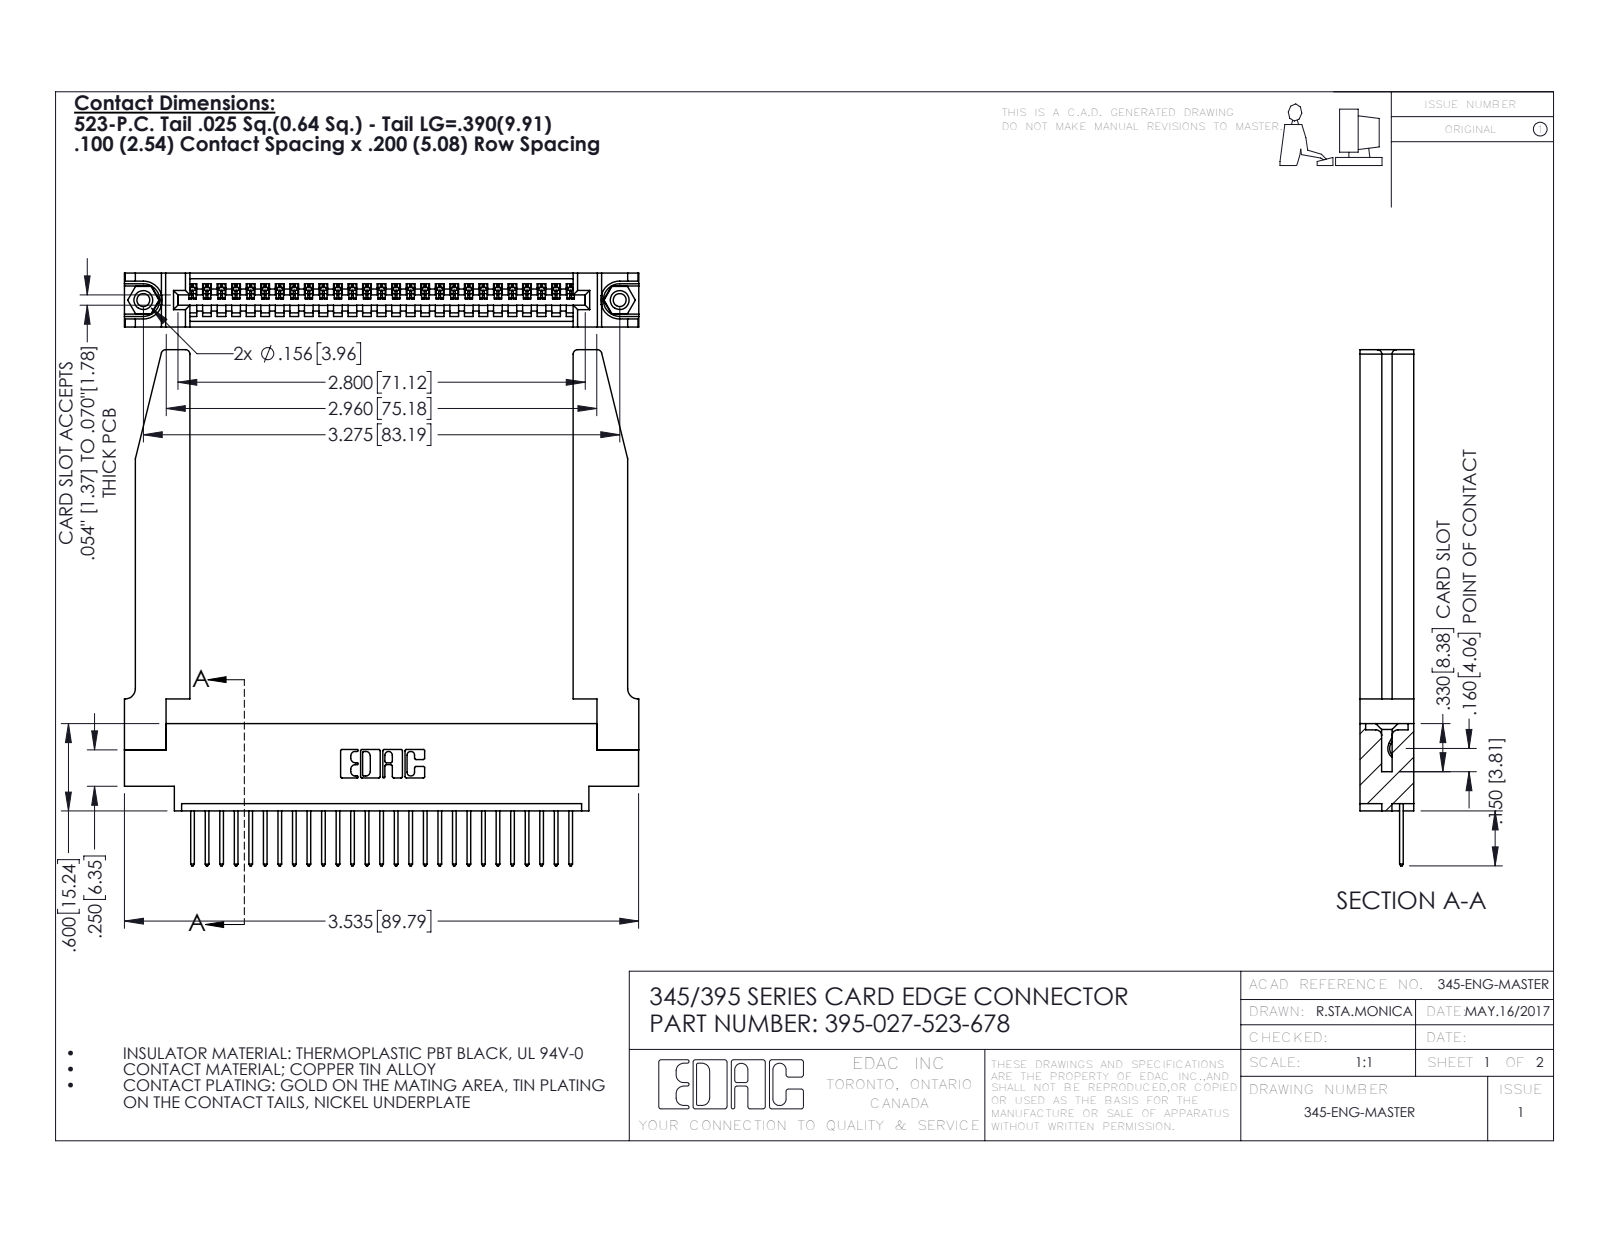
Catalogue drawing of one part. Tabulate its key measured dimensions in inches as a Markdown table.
| quantity | value |
| --- | --- |
| part name | 395-027-523-678; 345-250-001_345-250-001-102; 345-292-001_345-293-123; 345 Part_0.170 Offset - 0.156 Dia-TH (+1 more) |
| STEP written by | SolidWorks 2016 (CONFIG_CONTROL_DESIGN) |
| units | inches |
| bodies | 32 solids, 1930 faces (1306 planar, 572 cylindrical, 52 other) |
| overall size | 3.547 × 3.536 × 0.37 |
| volume | 0.98 in³ |
| surface area | 27.6 in² |
| round holes (diameter × count) | 0.089 × 2, 0.125 × 2, 0.156 × 2, 0.064 × 1 |
| round bosses / shafts (diameter × count) | 0.155 × 2 |
| partial cylindrical surfaces (radius × count) | 0.006 × 54, 0.01 × 54, 0.01 × 22, 0.03 × 8, 0.007 × 6, 0.031 × 6, 0.026 × 3, 0.031 × 2 |
| main face-to-face distances | 0.37, 0.072, 0.298, 0.098, 0.272, 0.025, 0.2, 0.148, 0.15, 0.225 |
| hole center spacings | 0.27, 3.04, 3.275 |
